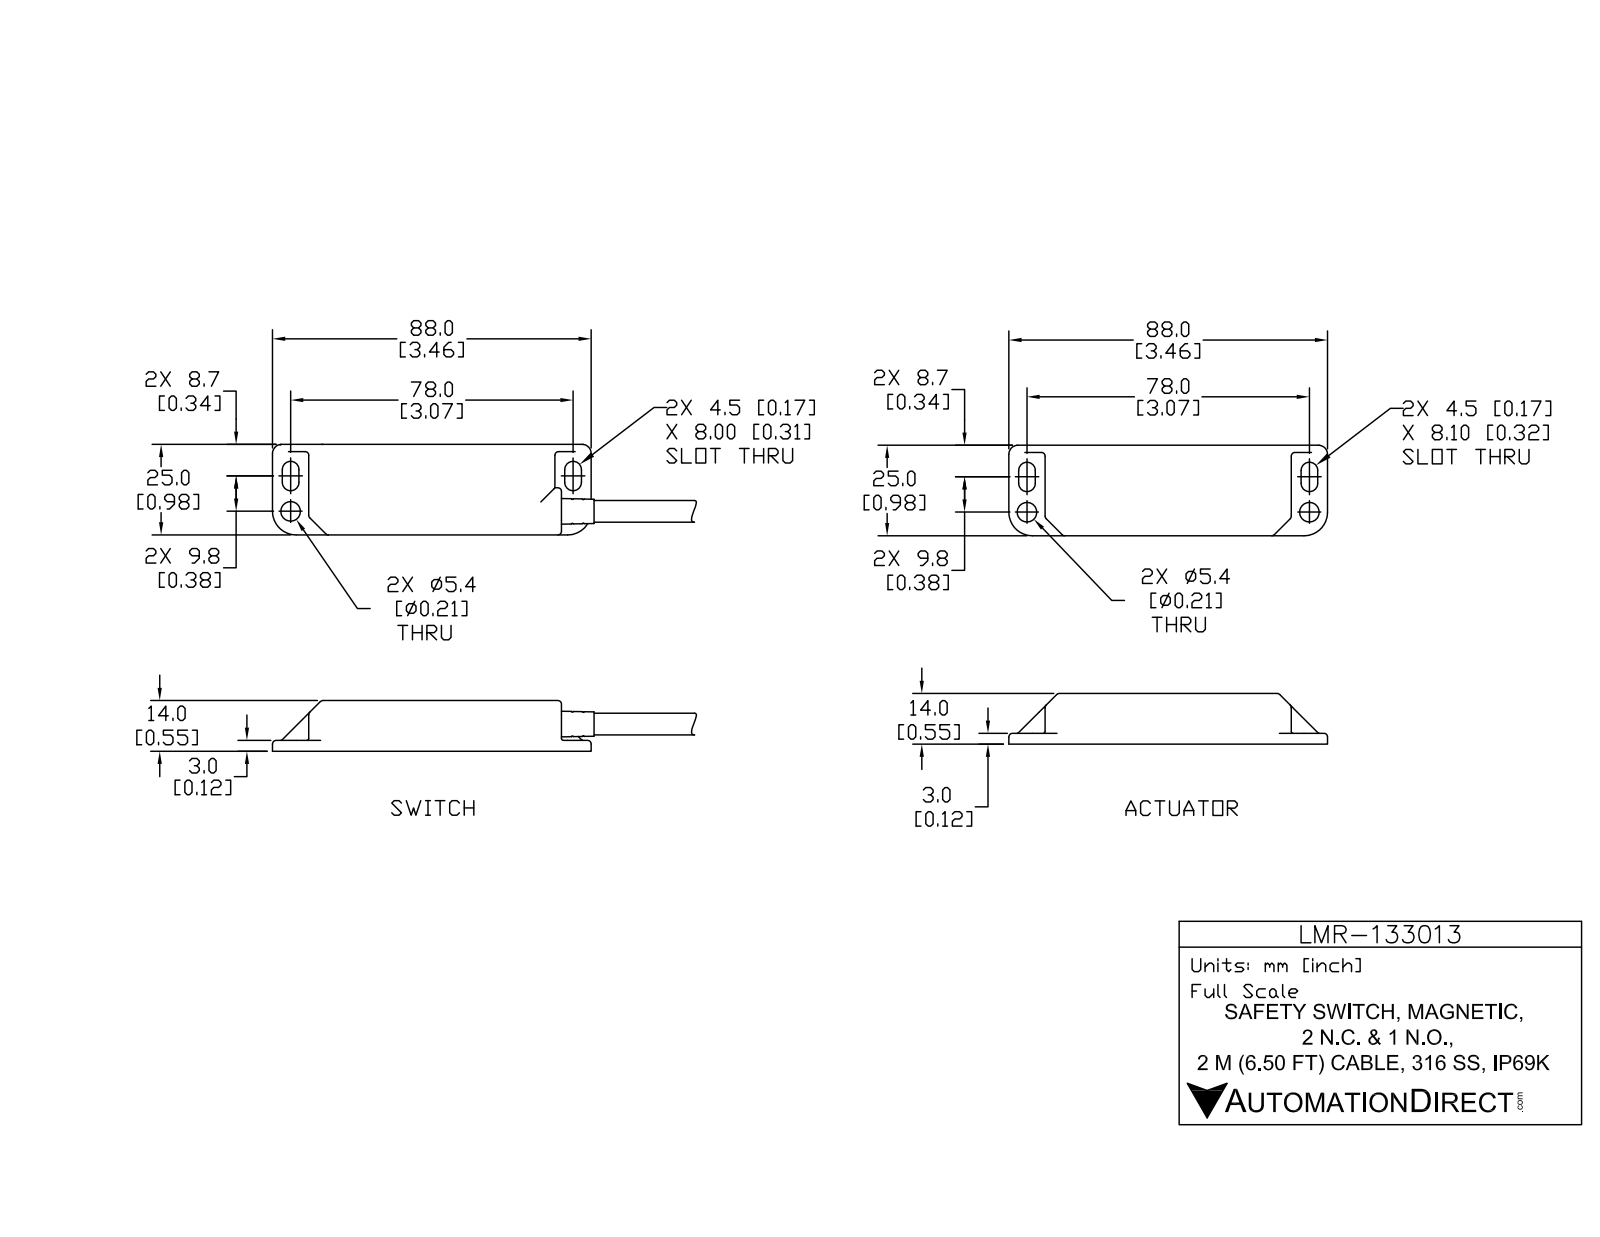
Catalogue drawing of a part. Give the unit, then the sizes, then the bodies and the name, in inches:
Units: inches
Overall size (bounding box): 9.173 × 2.008 × 0.551
Round holes (diameter × count): ⌀0.197 ×4, ⌀0.213 ×4, ⌀0.232 ×1, ⌀0.283 ×1
Round bosses / shafts (diameter × count): ⌀0.079 ×4, ⌀0.193 ×2, ⌀0.134 ×2, ⌀0.339 ×1, ⌀0.299 ×1, ⌀0.28 ×1, ⌀0.236 ×1
Partial cylindrical surfaces — rounded edges, fillets, slot ends (radius × count): R0.02 ×95, R0.039 ×45, R0.091 ×8, R0.098 ×4, R0.256 ×4, R0.193 ×1
Main face-to-face distances: 0.067, 0.055, 0.543, 1.024, 0.476, 0.488, 0.421, 0.917, 0.106, 0.039
Hole centre spacings: 0.67, 1.172, 1.181, 1.243, 1.496, 1.687, 1.815, 1.907
Volume: 1.659 in³ · Surface area: 46.33 in²
Bodies: 10 solids, 676 faces (194 planar, 244 cylindrical, 238 other)
Part name (STEP PRODUCT): LMR-133013_2; LMR-133013_1; LMR-133013
STEP written by: SolidWorks 2017 (AUTOMOTIVE_DESIGN)
